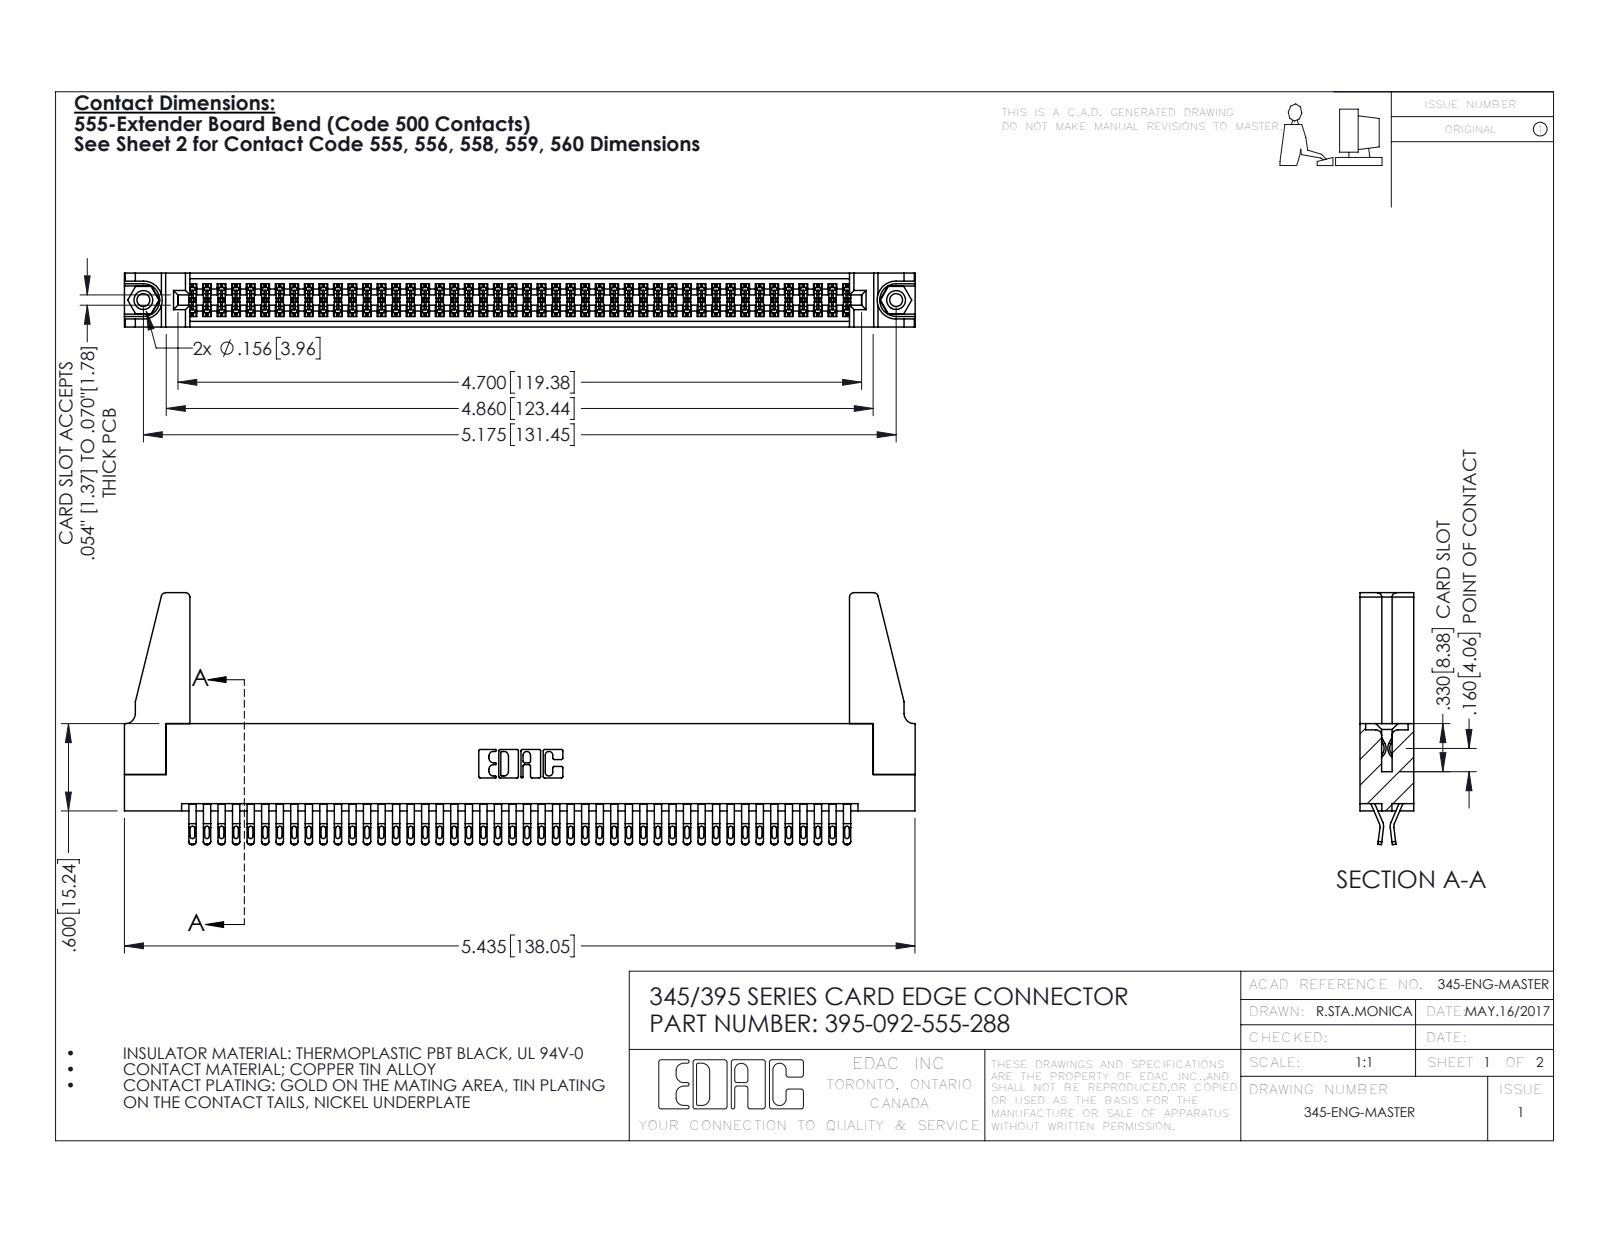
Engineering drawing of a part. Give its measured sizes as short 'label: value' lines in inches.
name: 345 Part_Flush Mounting Lugs - 0.156 Dia-TH; 345-250-001_345-250-001-102; 395-092-555-288; 345-220-078_345-220-088 (+1 more)
written by: SolidWorks 2016 (CONFIG_CONTROL_DESIGN)
unit: in
bodies: 97 solids, 5402 faces (3004 planar, 2382 cylindrical, 16 other)
size: 5.436 × 1.732 × 0.37
volume: 1.036 in³; area: 37.83 in²
holes: 2× ⌀0.089, 2× ⌀0.125, 2× ⌀0.156, 1× ⌀0.064
bosses: 2× ⌀0.155
rounds: 230× R0.016, 184× R0.02, 138× R0.006, 22× R0.01, 8× R0.03, 6× R0.007, 6× R0.031, 3× R0.026
face distances: 0.072, 0.298, 0.37, 0.025, 0.2, 0.098, 0.272, 0.225, 0.175, 0.149
hole spacings: 0.27, 4.939, 5.175
